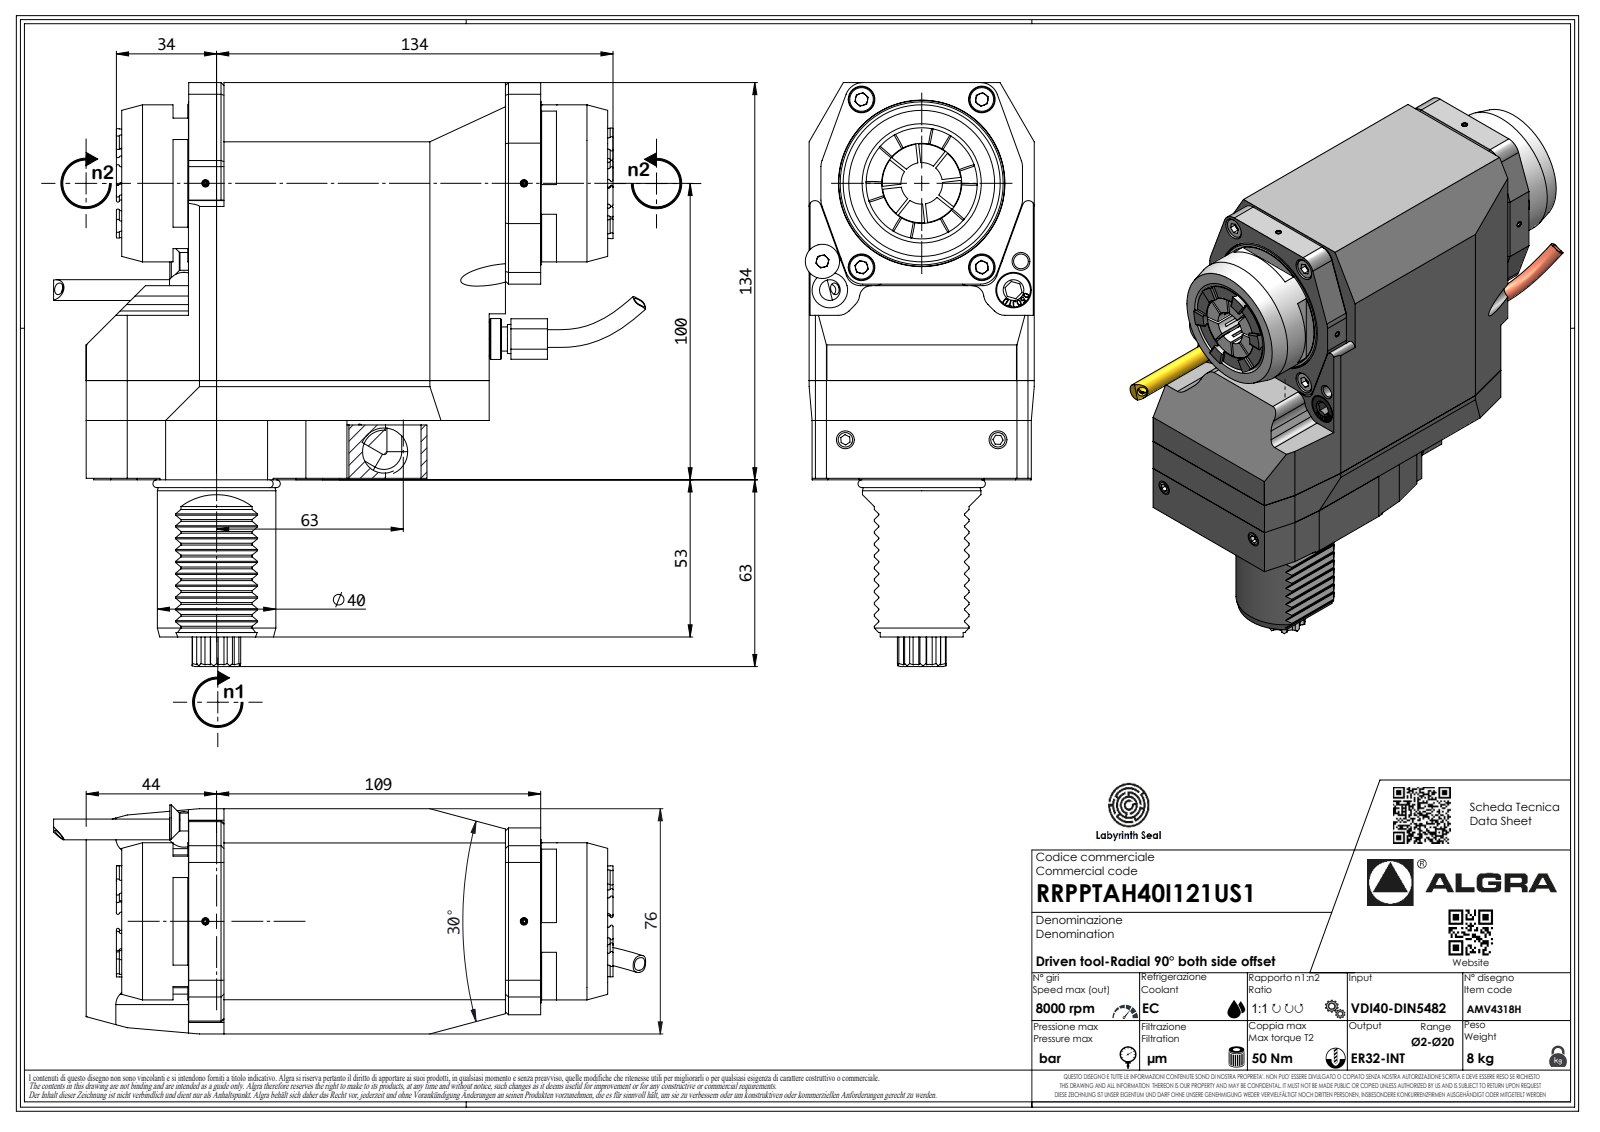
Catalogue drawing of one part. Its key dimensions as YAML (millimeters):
part_name: "RRPPTAH40I121US1"
step_written_by: "SolidWorks 2023 (AUTOMOTIVE_DESIGN)"
units: millimeters
bodies: {solids: 1, faces: 675, planar: 469, cylindrical: 112, other: 94}
overall_size: [199.81, 197, 76]
volume: 1311000
surface_area: 94346
round_holes:
  - {diameter: 2.1, count: 1}
  - {diameter: 4, count: 1}
  - {diameter: 5, count: 1}
round_bosses_or_shafts:
  - {diameter: 53, count: 1}
  - {diameter: 40, count: 1}
  - {diameter: 38.7, count: 1}
  - {diameter: 9.8, count: 1}
  - {diameter: 8.15, count: 1}
  - {diameter: 7, count: 1}
  - {diameter: 6.37, count: 1}
  - {diameter: 1.7, count: 1}
partial_cylinders:
  - {radius: 0.3, count: 22}
  - {radius: 6, count: 10}
  - {radius: 0.33, count: 7}
  - {radius: 0.52, count: 7}
  - {radius: 3.7, count: 7}
  - {radius: 5, count: 6}
  - {radius: 3, count: 4}
  - {radius: 2, count: 3}
face_to_face_distances: [76, 0.5, 12, 134, 20, 114, 22.6, 141.4, 68.5, 65.5]
